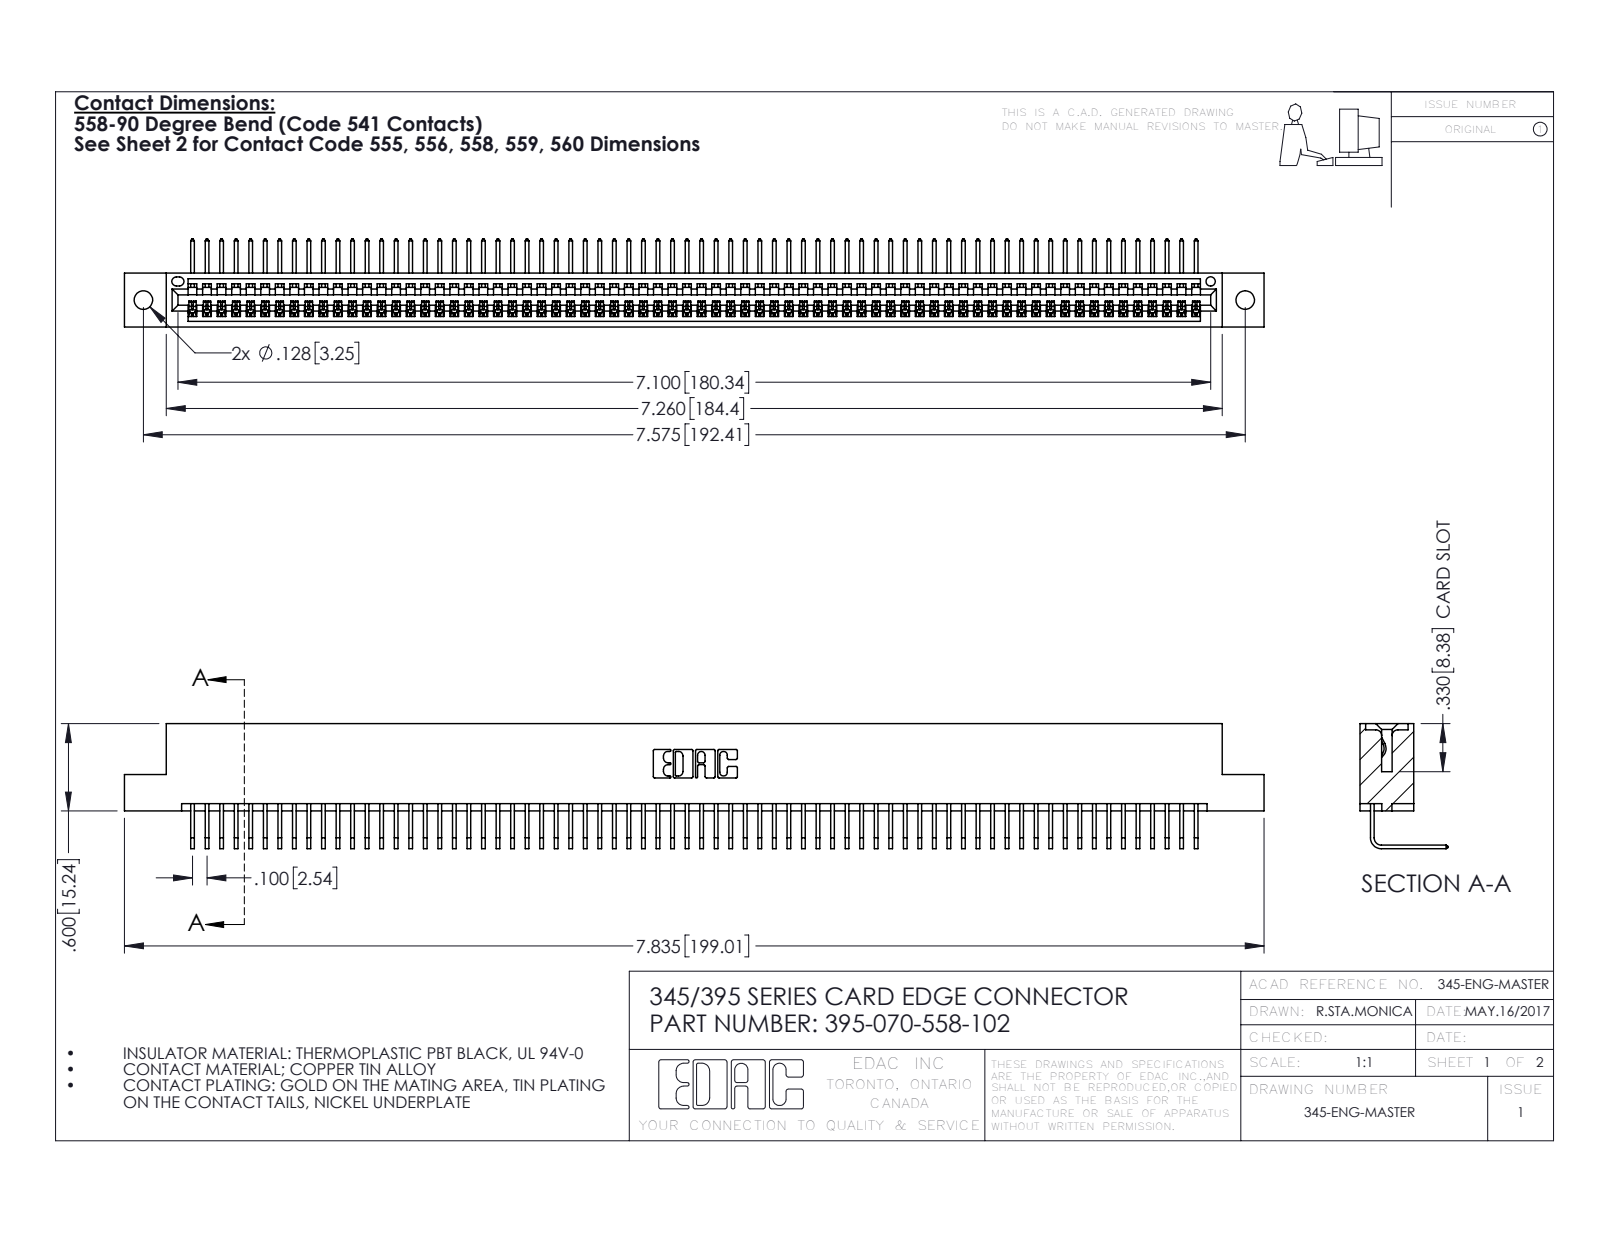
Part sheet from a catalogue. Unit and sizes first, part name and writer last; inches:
Units: inches
Overall size (bounding box): 7.835 × 0.859 × 0.605
Round holes (diameter × count): ⌀0.128 ×2, ⌀0.064 ×1
Partial cylindrical surfaces — rounded edges, fillets, slot ends (radius × count): R0.006 ×140, R0.01 ×22, R0.007 ×6, R0.031 ×6, R0.026 ×3, R0.031 ×2, R0.04 ×2, R0.014 ×1
Main face-to-face distances: 0.298, 0.072, 0.37, 0.2, 0.098, 0.272, 0.025, 0.225, 0.149, 0.072
Hole centre spacings: 0.27, 7.339, 7.575
Volume: 1.179 in³ · Surface area: 42.11 in²
Bodies: 71 solids, 4326 faces (3020 planar, 1306 cylindrical, 0 other)
Part name (STEP PRODUCT): 395-070-558-102; 345 Part_Flush Mounting Lugs - 0.128 Dia; 345-292-001_558 Tail - 2
STEP written by: SolidWorks 2016 (CONFIG_CONTROL_DESIGN)
